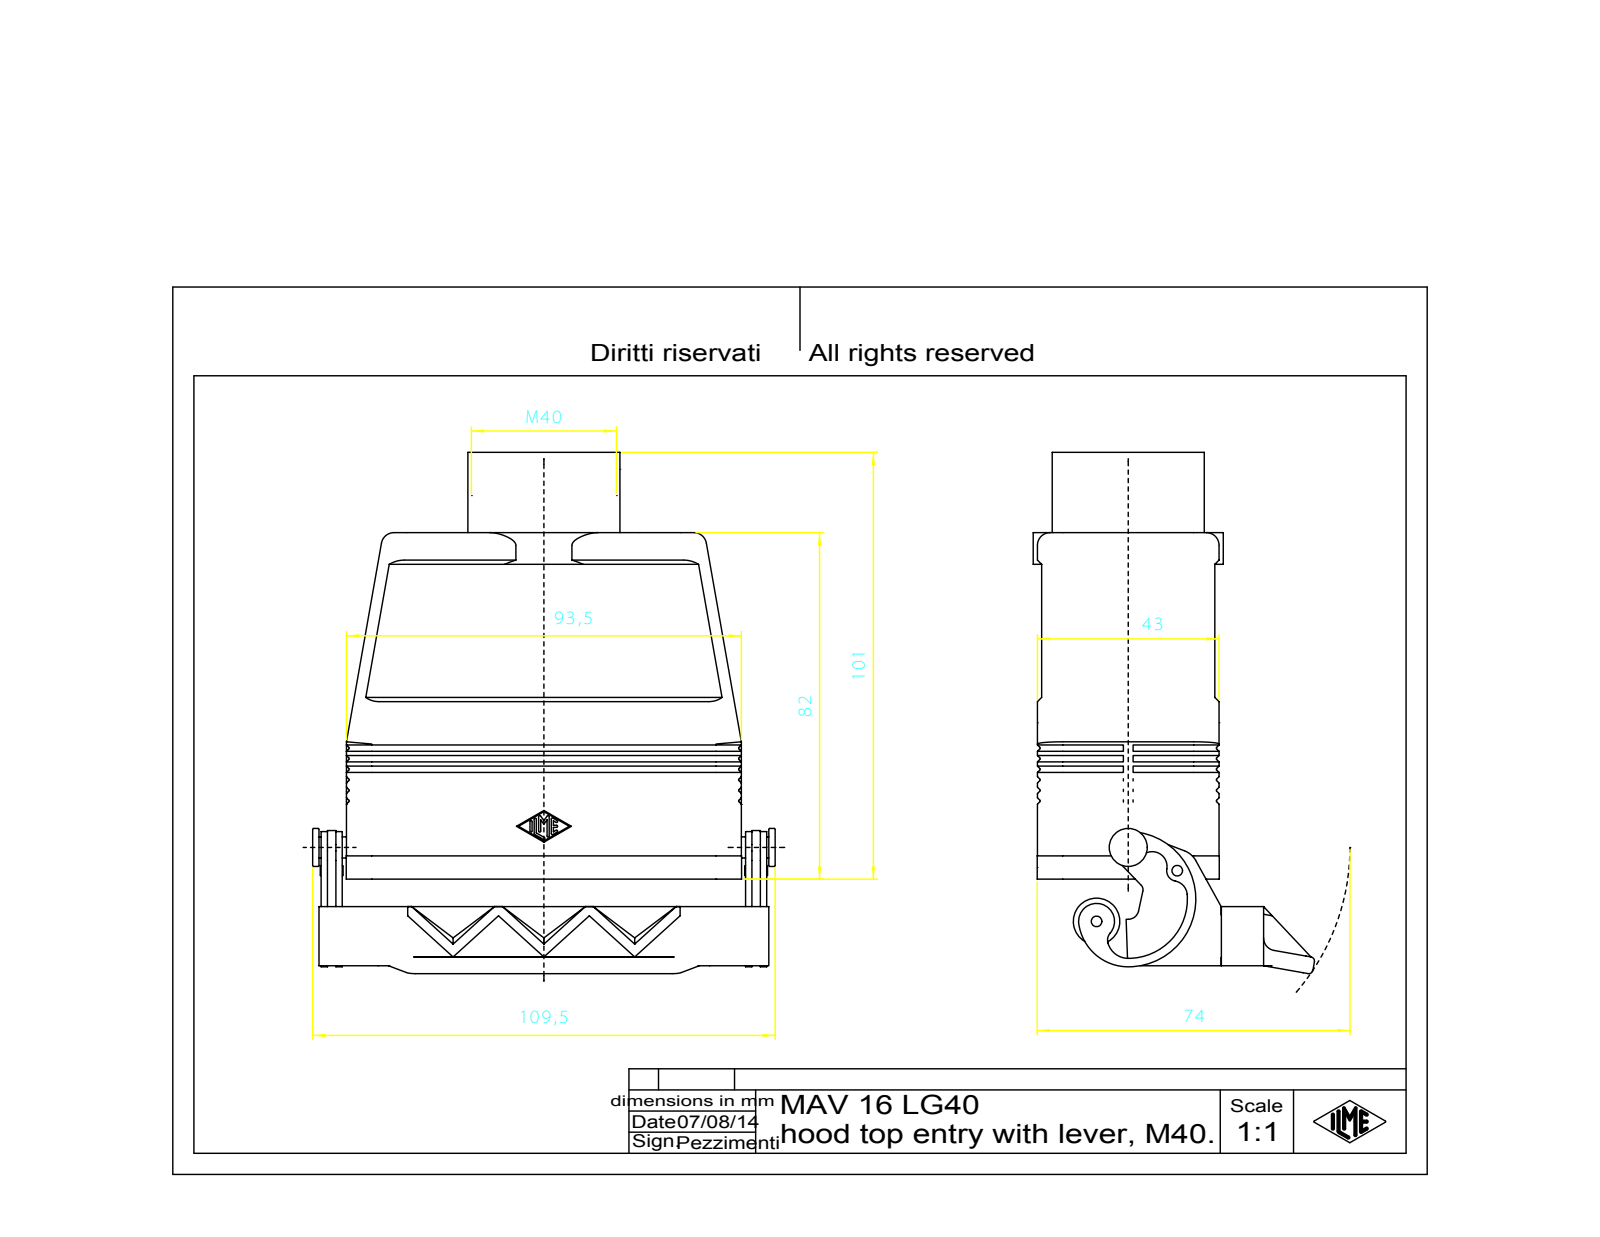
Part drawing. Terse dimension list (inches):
name: MAV_16_LG40
written by: Creo Elements/Direct Modeling 18.0B 02-Dec-2011 (C) Parametric Technology GmbH (AUTOMOTIVE_DESIGN)
unit: in
bodies: 1 solid, 800 faces (351 planar, 258 cylindrical, 191 other)
size: 4.857 × 4.311 × 2.641
volume: 6.542 in³; area: 97.39 in²
holes: 4× ⌀0.079, 4× ⌀0.122, 1× ⌀0.098, 1× ⌀1.339, 1× ⌀1.575
bosses: 1× ⌀1.811, 1× ⌀1.772, 1× ⌀0.433, 1× ⌀0.354, 1× ⌀0.197, 1× ⌀0.122, 1× ⌀0.079
rounds: 38× R0.01, 28× R0.008, 9× R0.098, 8× R0.236, 7× R0.118, 6× R0.039, 5× R0.059, 4× R0.096
face distances: 0.138, 0.136, 1.557, 0.096, 0.039, 1.518, 0.098, 1.555, 1.654, 1.516
hole spacings: 1.615, 1.063, 3.051, 3.231
